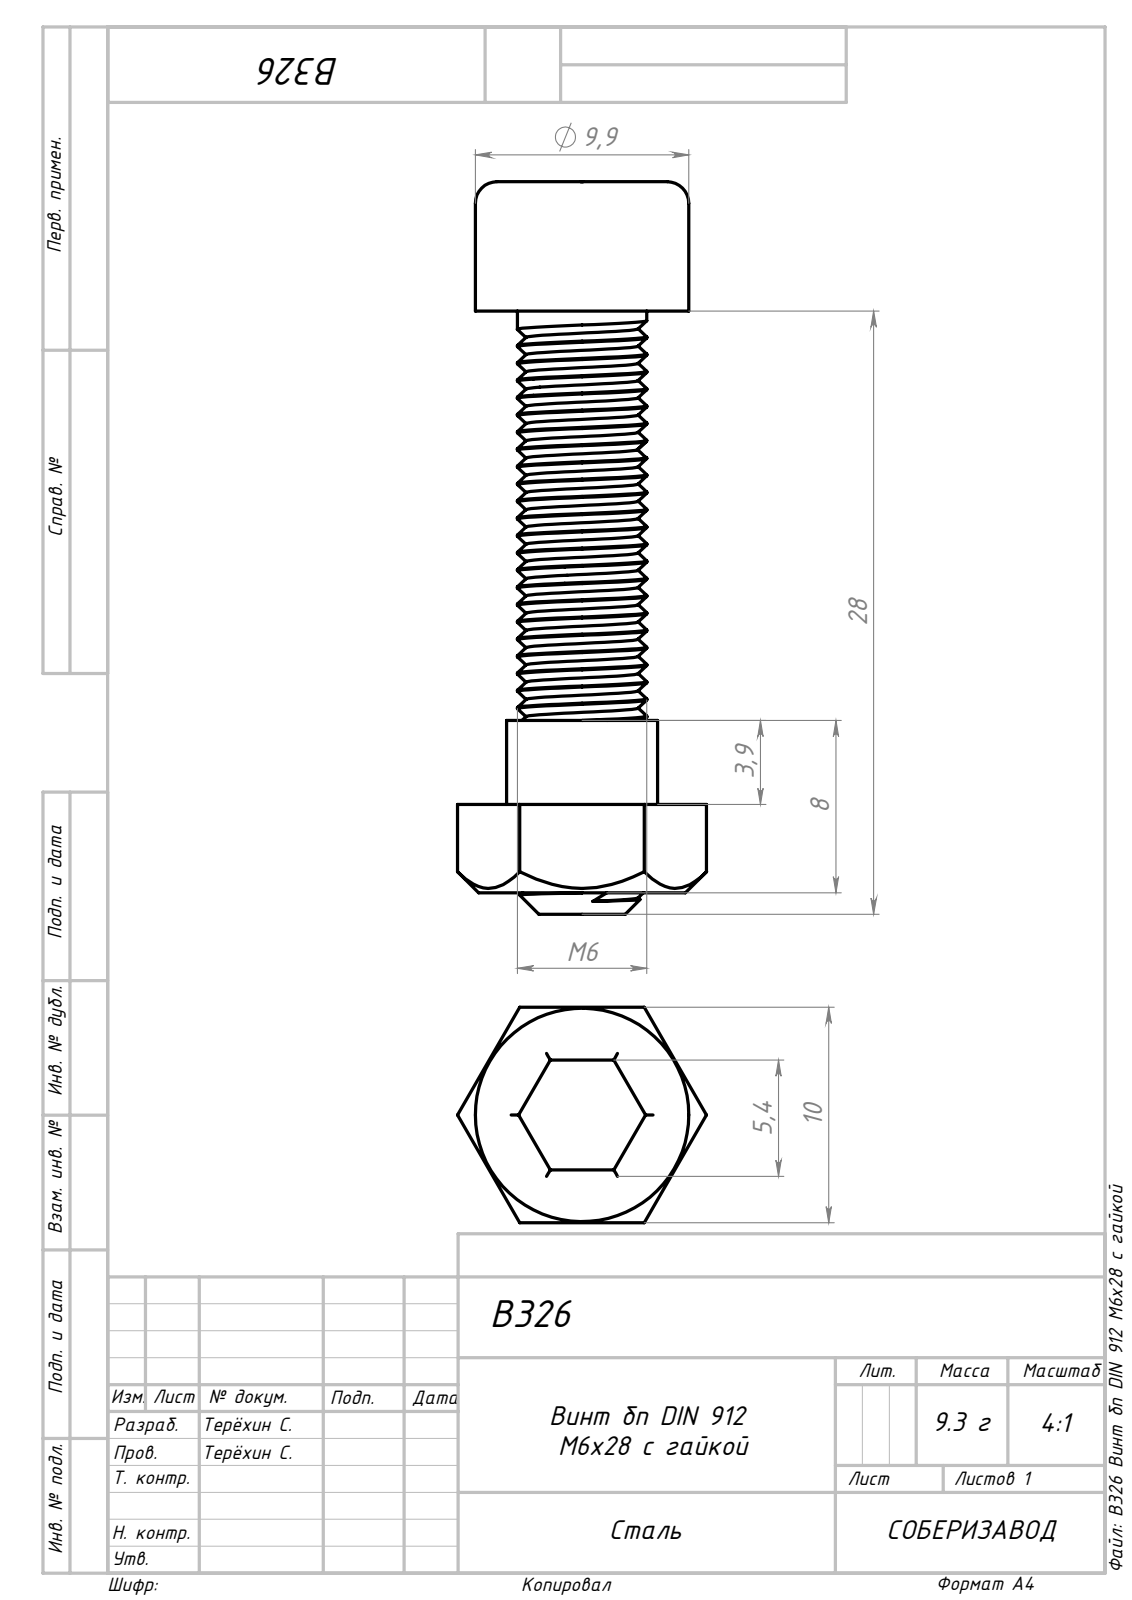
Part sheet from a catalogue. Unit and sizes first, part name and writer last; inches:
Units: inches
Overall size (bounding box): 1.339 × 0.455 × 0.394
Round holes (diameter × count): ⌀0.209 ×1
Round bosses / shafts (diameter × count): ⌀0.39 ×1, ⌀0.276 ×1, ⌀0.236 ×1
Partial cylindrical surfaces — rounded edges, fillets, slot ends (radius × count): R0.012 ×6
Main face-to-face distances: 0.096, 0.297, 0.394, 0.902, 0.201, 0.161, 1.063, 1.142, 0.98, 0.079
Volume: 0.083 in³ · Surface area: 2.478 in²
Bodies: 2 solids, 152 faces (20 planar, 93 cylindrical, 39 other)
Part name (STEP PRODUCT): B326 Винт бп DIN 912 М6х28 с гайкой
STEP written by: SolidWorks 2022 (AUTOMOTIVE_DESIGN)
